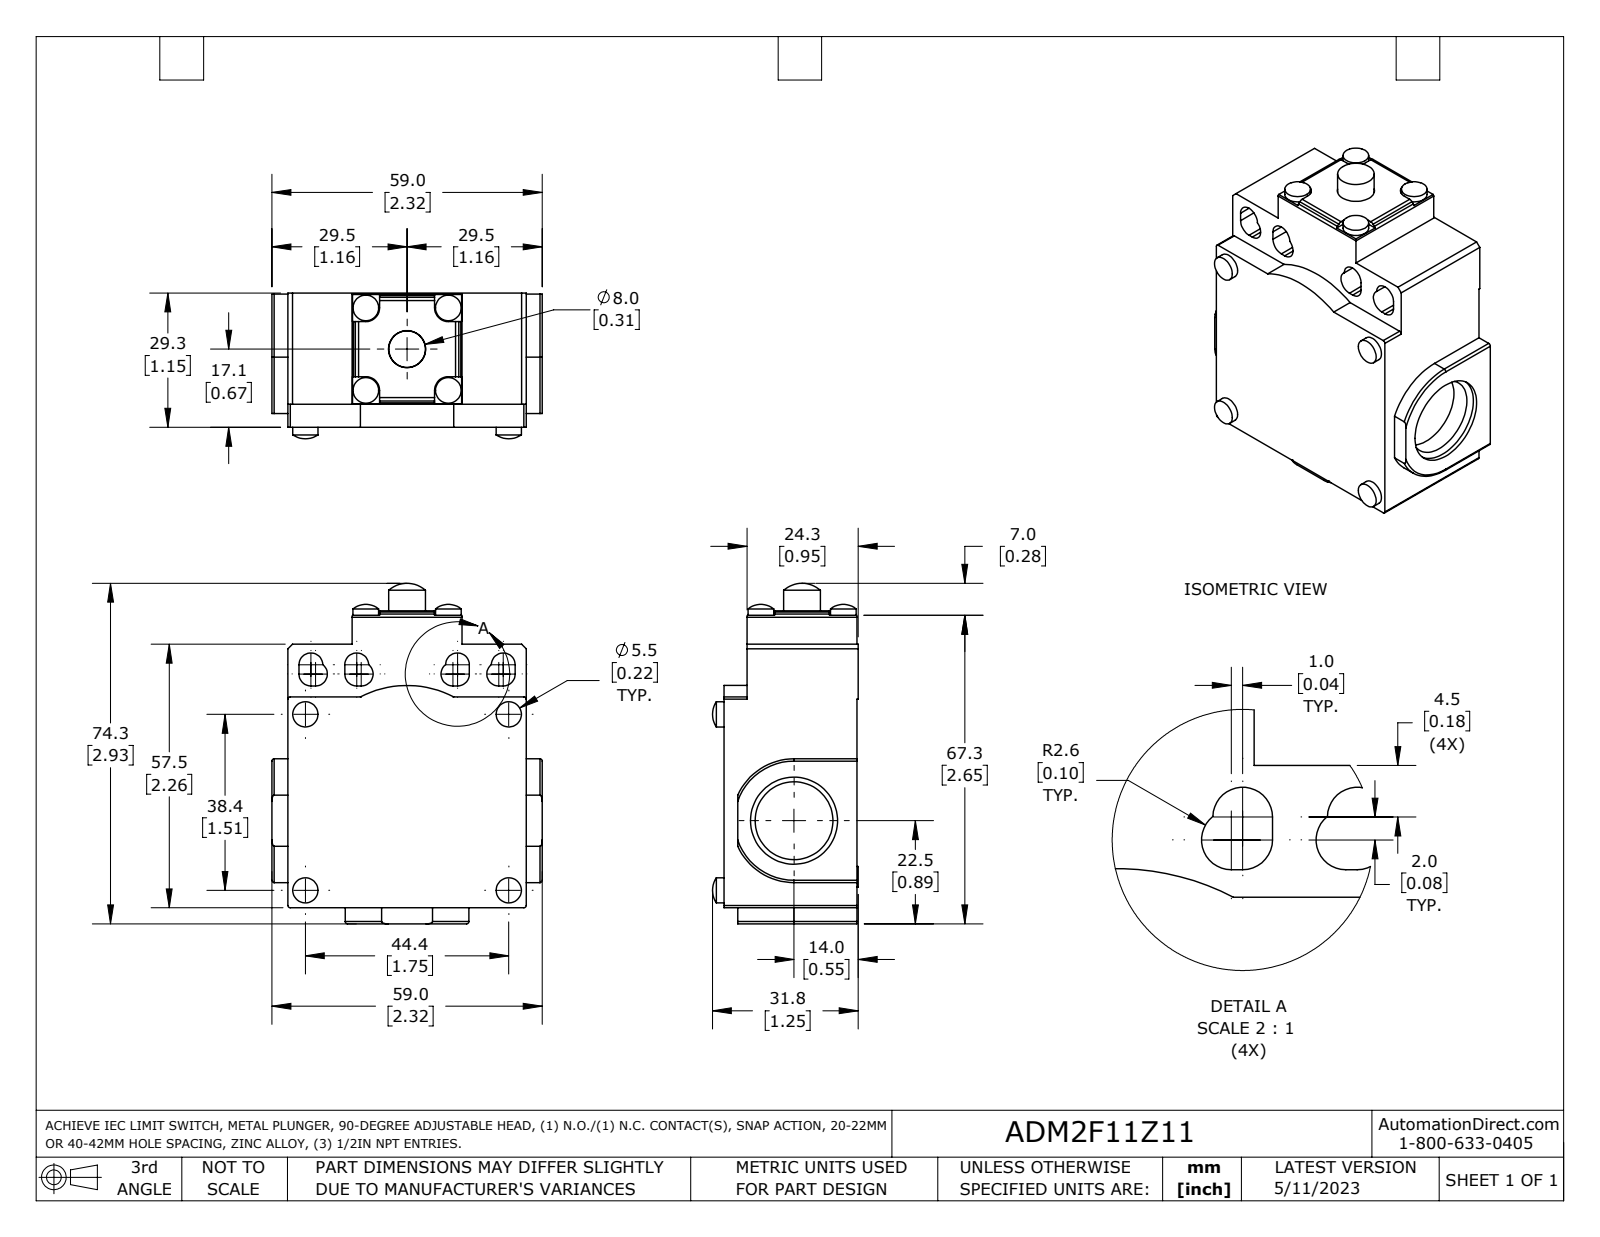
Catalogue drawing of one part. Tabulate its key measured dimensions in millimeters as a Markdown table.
| quantity | value |
| --- | --- |
| part name | ADM2F11Z11 |
| STEP written by | SolidWorks 2021 (AUTOMOTIVE_DESIGN) |
| units | millimeters |
| bodies | 1 solid, 164 faces (80 planar, 66 cylindrical, 18 other) |
| overall size | 74.3 × 59 × 31.8 |
| volume | 87 850 mm³ |
| surface area | 17 270 mm² |
| round holes (diameter × count) | 17 × 2, 19 × 2, 8.1 × 1 |
| round bosses / shafts (diameter × count) | 5.6 × 4, 5.5 × 4, 8 × 1 |
| partial cylindrical surfaces (radius × count) | 2.6 × 12, 0.5 × 10, 1 × 8, 3 × 4, 13.5 × 2, 10 × 1, 10.2 × 1, 22 × 1 |
| main face-to-face distances | 29.1, 3.5, 52, 6, 24, 2.5, 29.3, 55.5, 57.5, 49.5 |
| hole center spacings | 1.8 |
